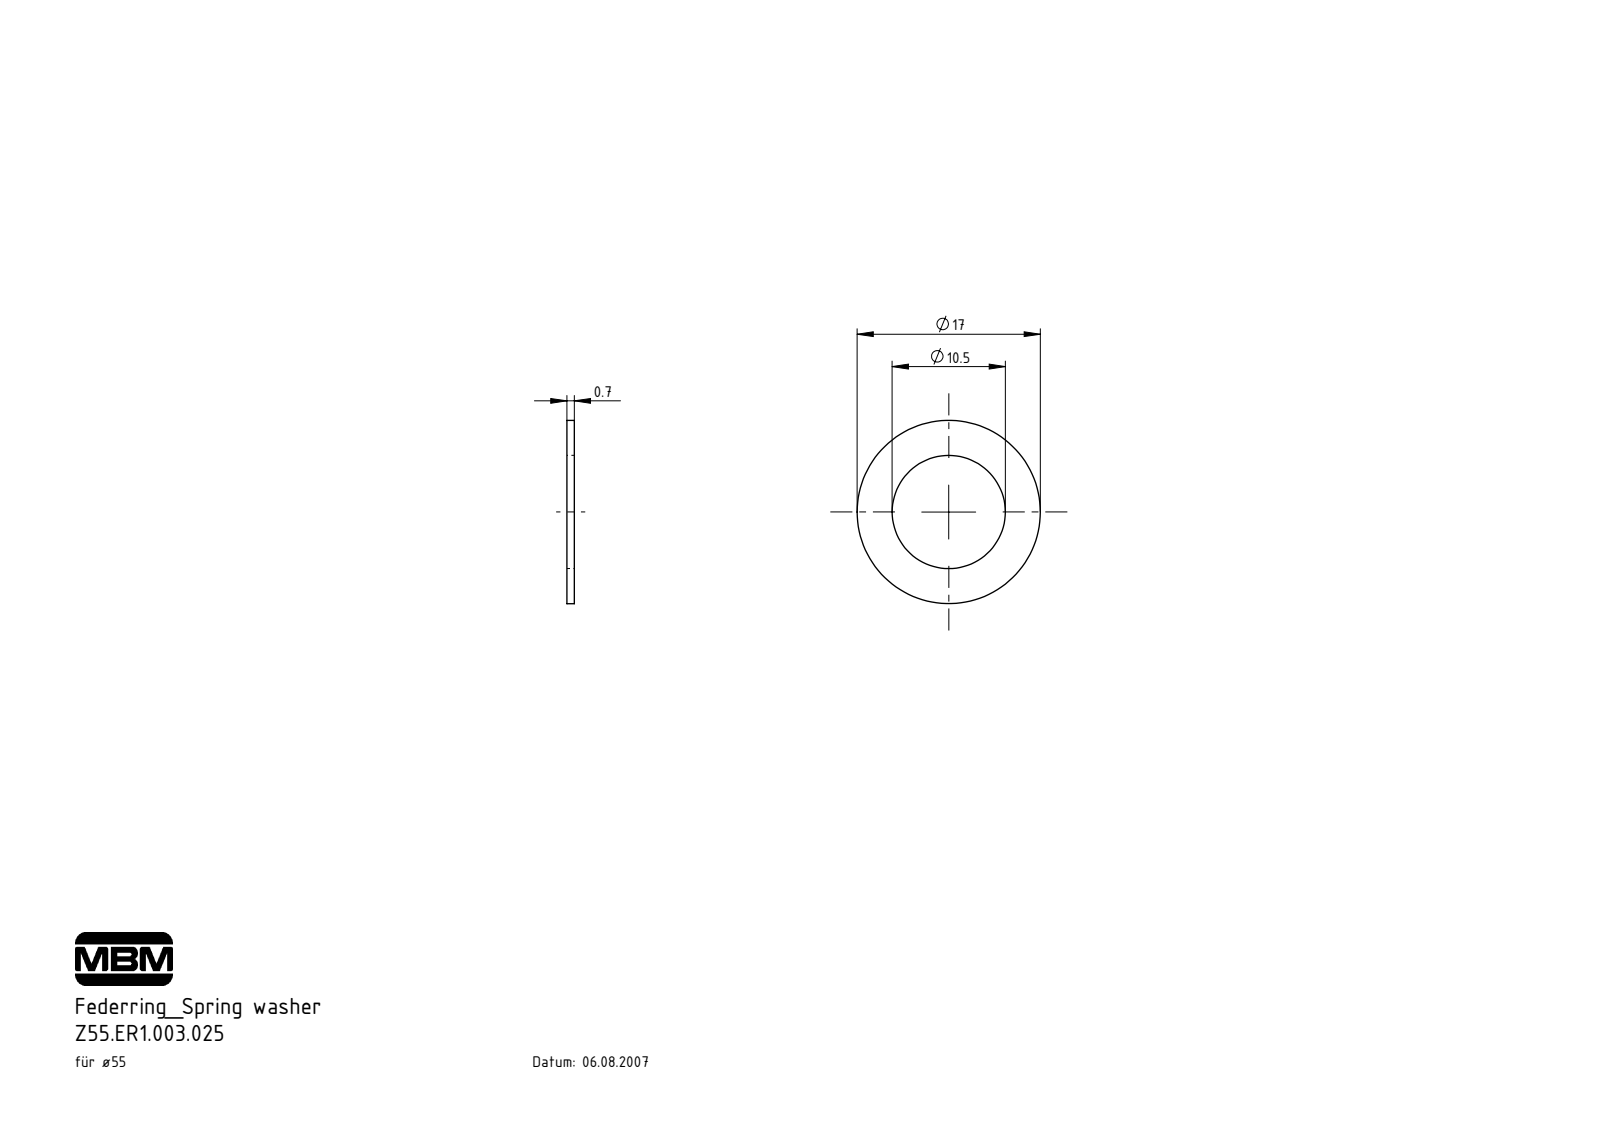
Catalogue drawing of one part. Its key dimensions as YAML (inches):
part_name: "Z55.ER1.003.025"
step_written_by: "SolidWorks 2017 (AUTOMOTIVE_DESIGN)"
units: inches
bodies: {solids: 1, faces: 6, planar: 2, cylindrical: 4, other: 0}
overall_size: [0.669, 0.669, 0.028]
volume: 0.006
surface_area: 0.529
round_holes:
  - {diameter: 0.413, count: 1}
round_bosses_or_shafts:
  - {diameter: 0.669, count: 1}
face_to_face_distances: [0.028]
